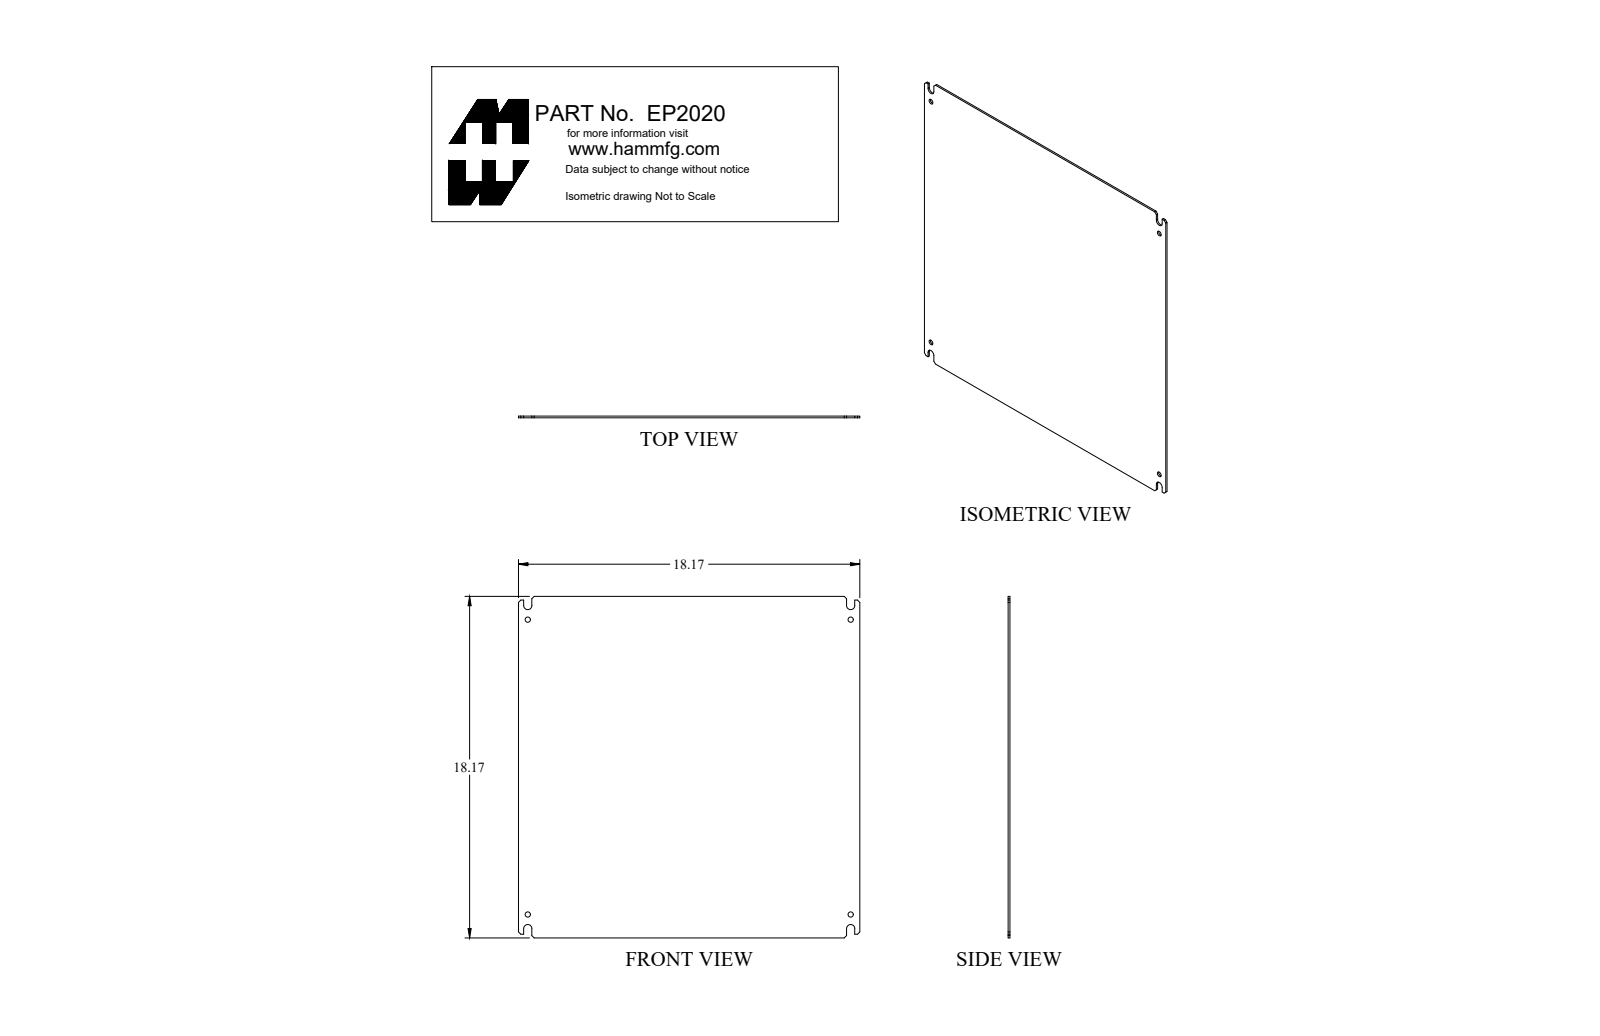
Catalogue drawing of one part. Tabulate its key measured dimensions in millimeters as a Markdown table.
| quantity | value |
| --- | --- |
| part name | EP2020 |
| STEP written by | SolidWorks 2018 (AUTOMOTIVE_DESIGN) |
| units | millimeters |
| bodies | 1 solid, 40 faces (26 planar, 14 cylindrical, 0 other) |
| overall size | 461.5 × 461.5 × 2.4 |
| volume | 511 300 mm³ |
| surface area | 428 600 mm² |
| round holes (diameter × count) | 7.1 × 4 |
| partial cylindrical surfaces (radius × count) | 5.6 × 4 |
| main face-to-face distances | 2.4, 461.5, 18, 443.5, 6.9, 454.6, 11.1, 436.6, 425.5, 9.2 |
| hole center spacings | 398.5, 436.6, 591.1 |
